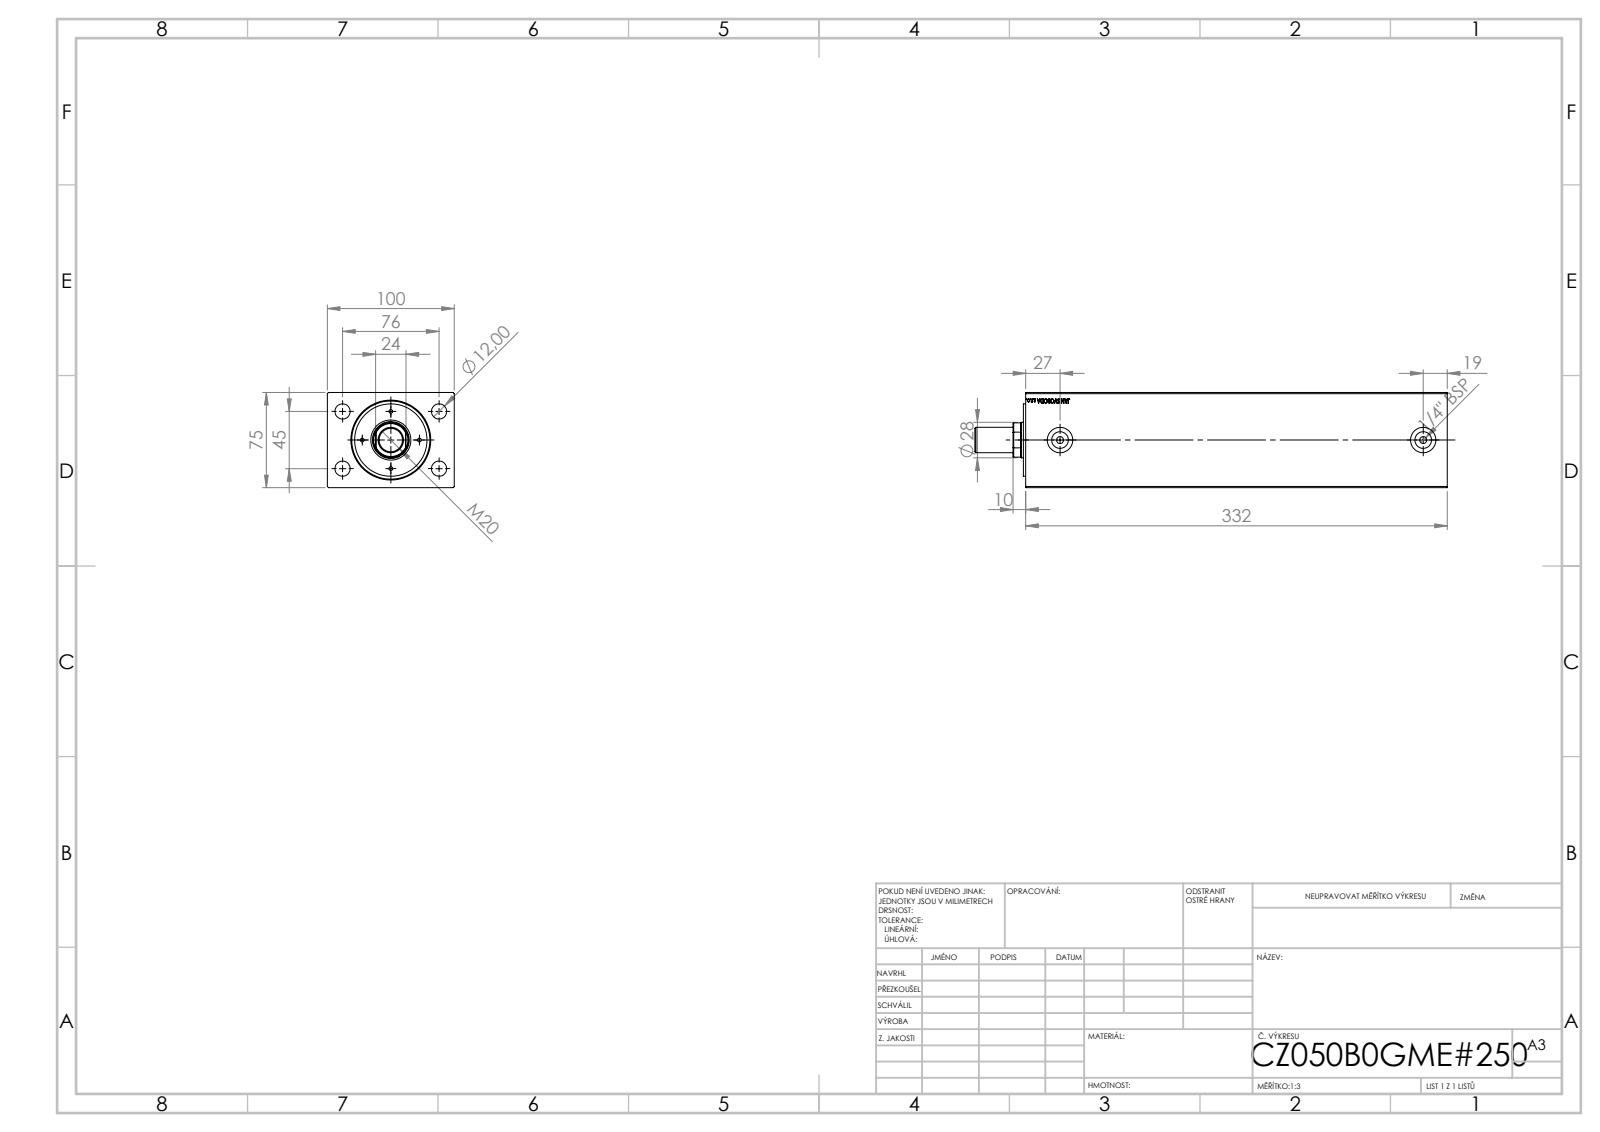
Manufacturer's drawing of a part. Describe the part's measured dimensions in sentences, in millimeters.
The part is named "V500CZ_SMALL_MALE_METRIC; V500CZ_B_VC; V500CZ". Its 3-D file was written by "SolidWorks 2019 (CONFIG_CONTROL_DESIGN)". It is 4 solids with 879 faces: 401 planar, 60 cylindrical and 418 other. Overall it measures 372 by 100 by 75 millimeters. Its volume is 2 232 000 cubic millimeters and its surface area 248 723 square millimeters. Round holes: 4 of diameter 3, 4 of diameter 12, 2 of diameter 5.5, 2 of diameter 13.16, 2 of diameter 20, 1 of diameter 18.5, 1 of diameter 28, 1 of diameter 29, 1 of diameter 36, 1 of diameter 50, 1 of diameter 61.5. Round bosses or shafts: 1 of diameter 57, 1 of diameter 20. Partial cylindrical surfaces (rounded edges, fillets, slot ends): 1 of radius 13.5. The main face-to-face distances are 75, 100, 332, 54, 278, 82, 196, 250, 1.8, 83.8. The hole center spacings are 22.5, 27.32, 31.82, 38, 44.16, 45, 58.9, 64.55.
